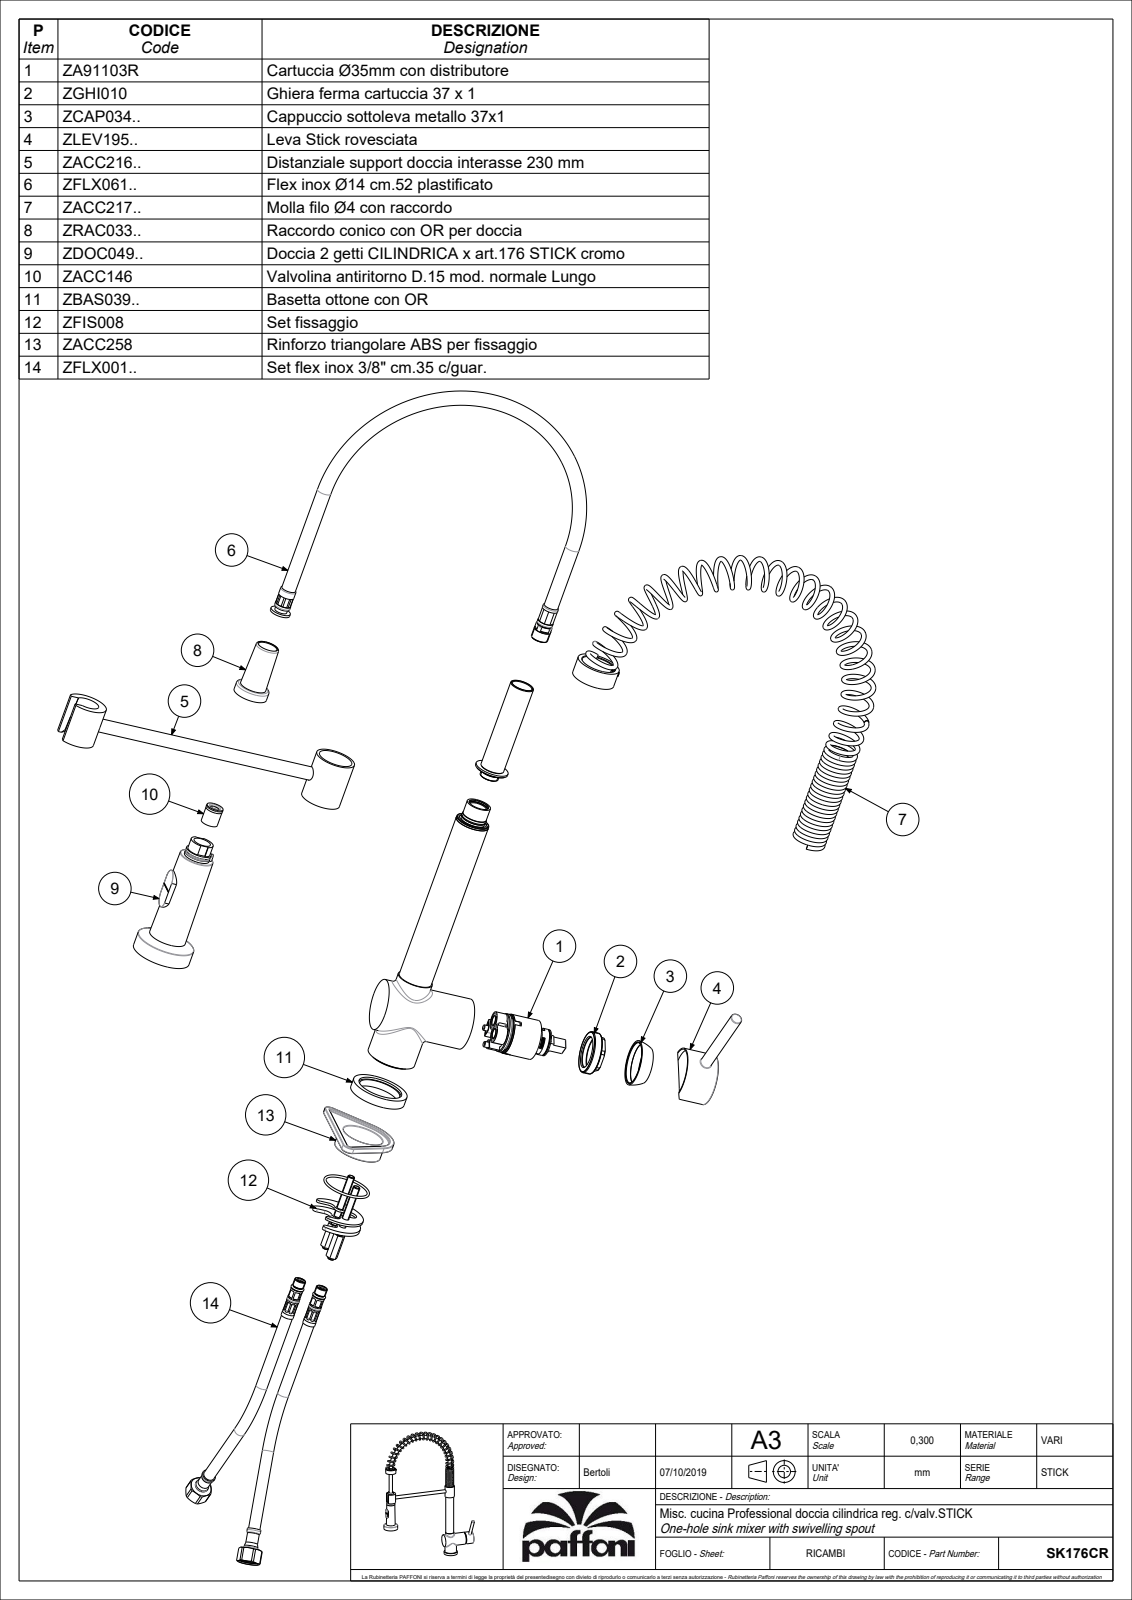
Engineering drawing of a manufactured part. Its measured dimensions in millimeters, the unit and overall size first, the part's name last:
Units: millimetres
Overall size (bounding box): 511.14 × 349.84 × 75.92
Round holes (diameter × count): ⌀3 ×1, ⌀5.6 ×1, ⌀6 ×1, ⌀12 ×1, ⌀15.2 ×1, ⌀17 ×1, ⌀18.6 ×1, ⌀26 ×1
Round bosses / shafts (diameter × count): ⌀2 ×32, ⌀13.5 ×2, ⌀51.5 ×1, ⌀49.5 ×1, ⌀45 ×1, ⌀44.5 ×1, ⌀43 ×1, ⌀38 ×1
Partial cylindrical surfaces — rounded edges, fillets, slot ends (radius × count): R0.5 ×8, R9.5 ×2, R0.1 ×1, R2 ×1, R2.25 ×1, R2.75 ×1, R10.15 ×1, R17.5 ×1
Main face-to-face distances: 123.3, 342.5, 219.2, 234.2, 357.5, 15, 108.2, 94, 14.2, 228.5
Volume: 669 386 mm³ · Surface area: 169 912 mm²
Bodies: 1 solid, 416 faces (106 planar, 160 cylindrical, 150 other)
Part name (STEP PRODUCT): SK176CR
STEP written by: CREO PARAMETRIC BY PTC INC, 2020044 (CONFIG_CONTROL_DESIGN)
